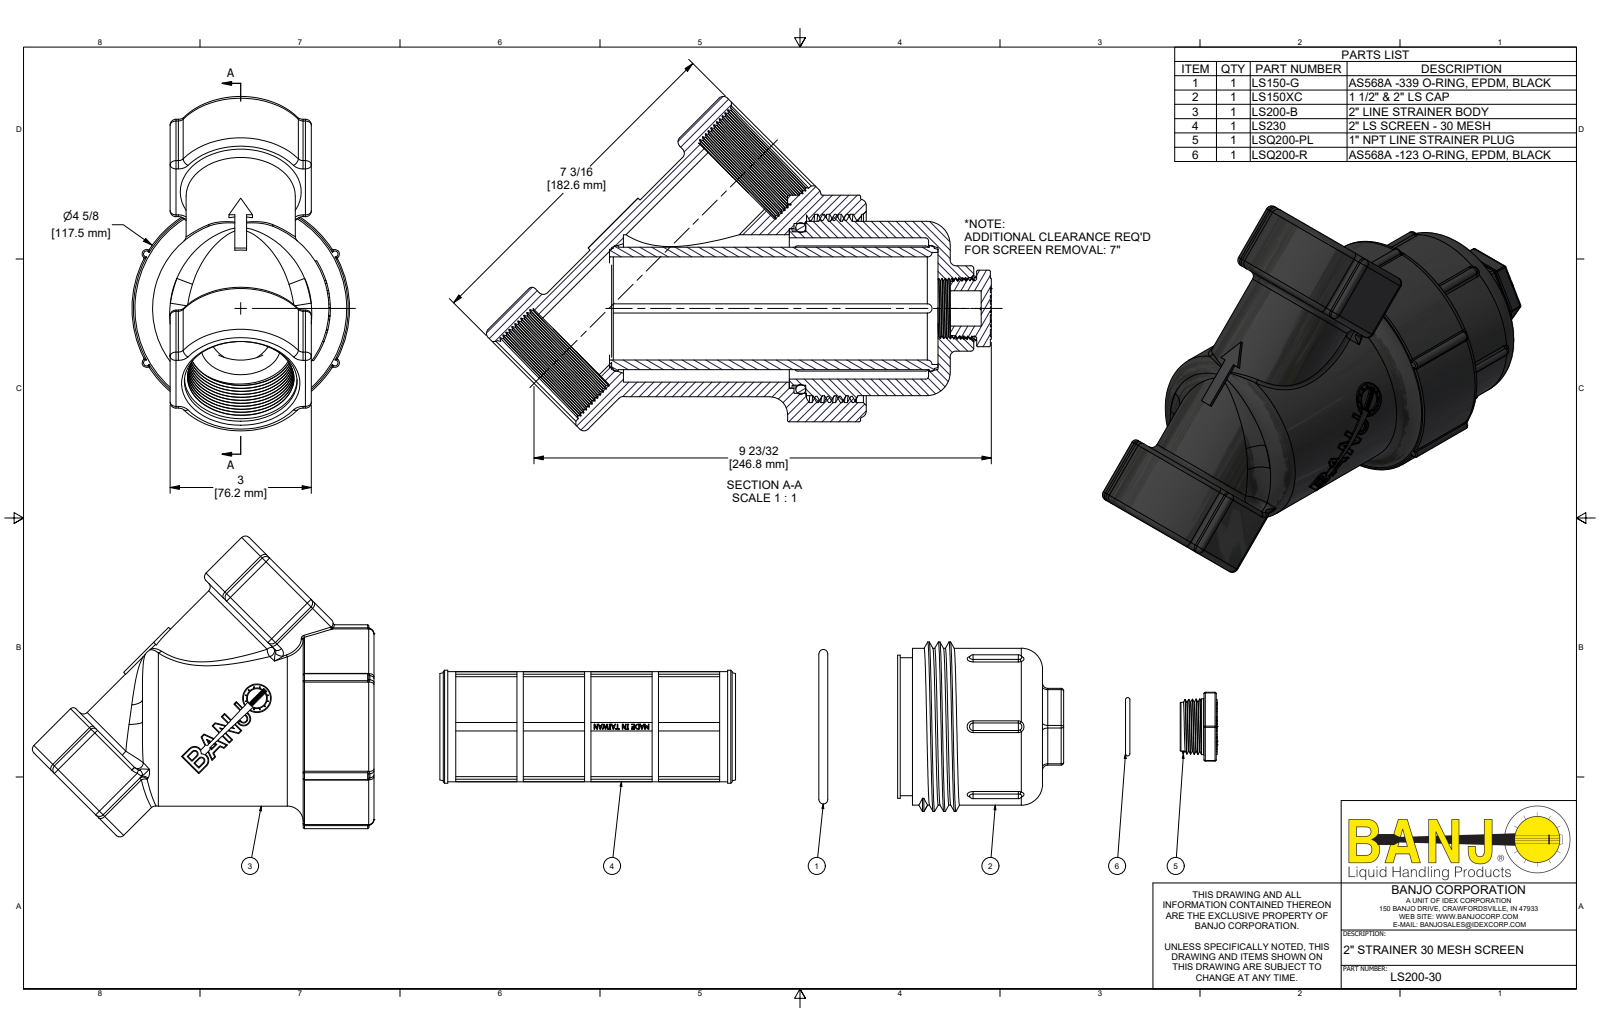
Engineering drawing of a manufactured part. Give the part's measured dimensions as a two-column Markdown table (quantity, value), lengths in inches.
| quantity | value |
| --- | --- |
| part name | LS200-30; LS200-B; LS150-C; LS150XC (+4 more) |
| STEP written by | Autodesk Inventor 2022 (AUTOMOTIVE_DESIGN) |
| units | inches |
| bodies | 6 solids, 1762 faces (849 planar, 277 cylindrical, 636 other) |
| overall size | 10.725 × 7.102 × 4.625 |
| volume | 54.12 in³ |
| surface area | 482.5 in² |
| round holes (diameter × count) | 1.7 × 2, 0.454 × 1, 0.641 × 1, 0.75 × 1, 2.19 × 1, 2.35 × 1, 3 × 1, 3.13 × 1, 3.395 × 1, 3.605 × 1, 3.729 × 1, 4 × 1 |
| round bosses / shafts (diameter × count) | 4.625 × 1, 3.75 × 1, 3.702 × 1, 3.38 × 1, 3.257 × 1, 2.666 × 1, 2.6 × 1, 2.38 × 1 |
| partial cylindrical surfaces (radius × count) | 0.06 × 46, 0.125 × 34, 0.03 × 30, 0.094 × 11, 0.1 × 4, 0.09 × 3, 0.065 × 2, 0.082 × 2 |
| main face-to-face distances | 1.34, 0.26, 3, 3.16, 2.785, 0.25, 1.445, 3.875, 0.2, 0.35 |
